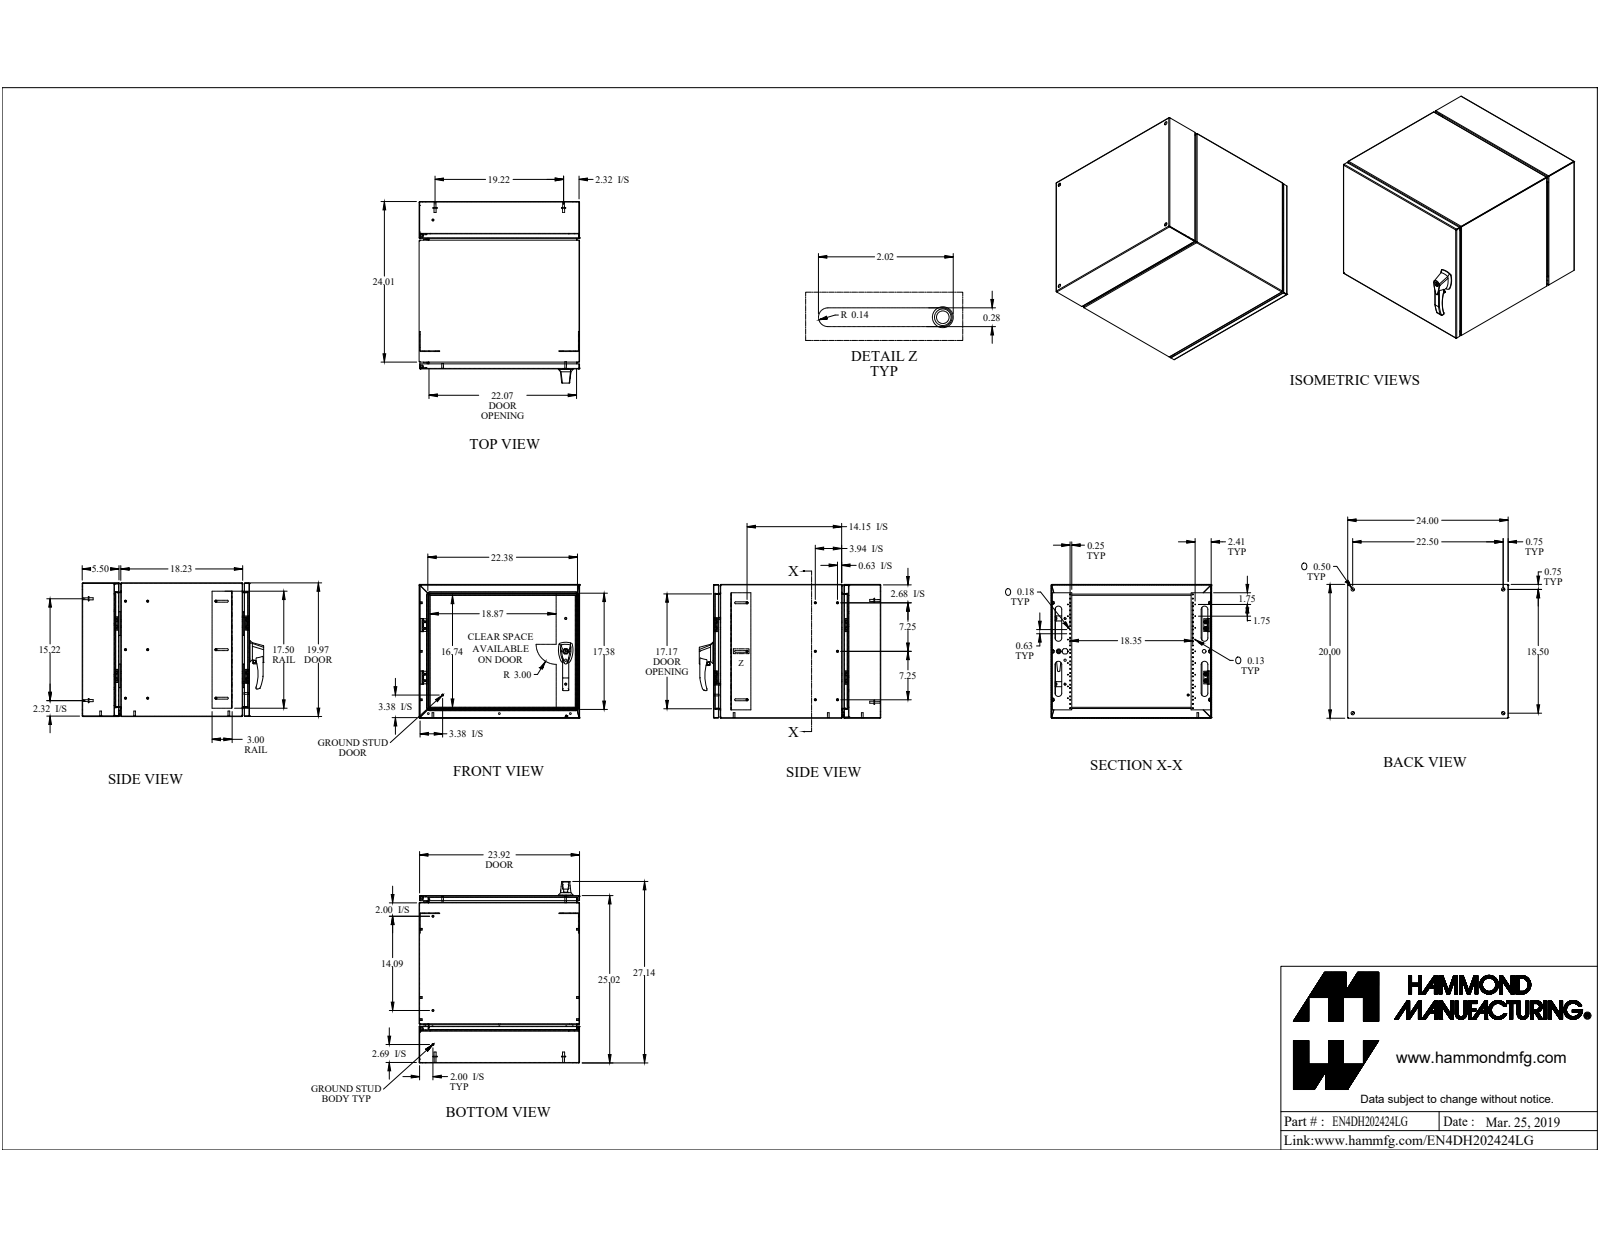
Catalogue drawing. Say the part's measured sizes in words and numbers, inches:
The part is named "EN4DH202424LG". Its 3-D file was written by "SolidWorks 2019 (CONFIG_CONTROL_DESIGN)". It is 177 solids with 3578 faces: 1968 planar, 899 cylindrical and 711 other. Overall it measures 27.135 by 24.001 by 20 inches. Its volume is 332.8 cubic inches and its surface area 8 634 square inches. Round holes: 60 of diameter 0.177, 18 of diameter 0.125, 15 of diameter 0.196, 15 of diameter 0.25, 8 of diameter 0.188, 8 of diameter 0.194, 8 of diameter 0.237, 7 of diameter 0.257, 7 of diameter 0.275, 5 of diameter 0.265, 4 of diameter 0.276, 4 of diameter 0.281. Round bosses or shafts: 24 of diameter 0.25, 16 of diameter 0.313, 10 of diameter 0.236, 9 of diameter 0.625, 8 of diameter 0.472, 8 of diameter 0.433, 8 of diameter 0.187, 6 of diameter 0.281. Partial cylindrical surfaces (rounded edges, fillets, slot ends): 38 of radius 0.036, 38 of radius 0.108, 18 of radius 0.141, 18 of radius 0.25, 17 of radius 0.125, 16 of radius 0.06, 12 of radius 0.079, 12 of radius 0.123. The main face-to-face distances are 0.072, 19.928, 24.948, 23.928, 19.856, 20, 23.856, 24.876, 25.02, 24. The hole center spacings are 3.5, 2.25, 7.25, 15.344, 1.125, 1.25, 2.375, 7.
